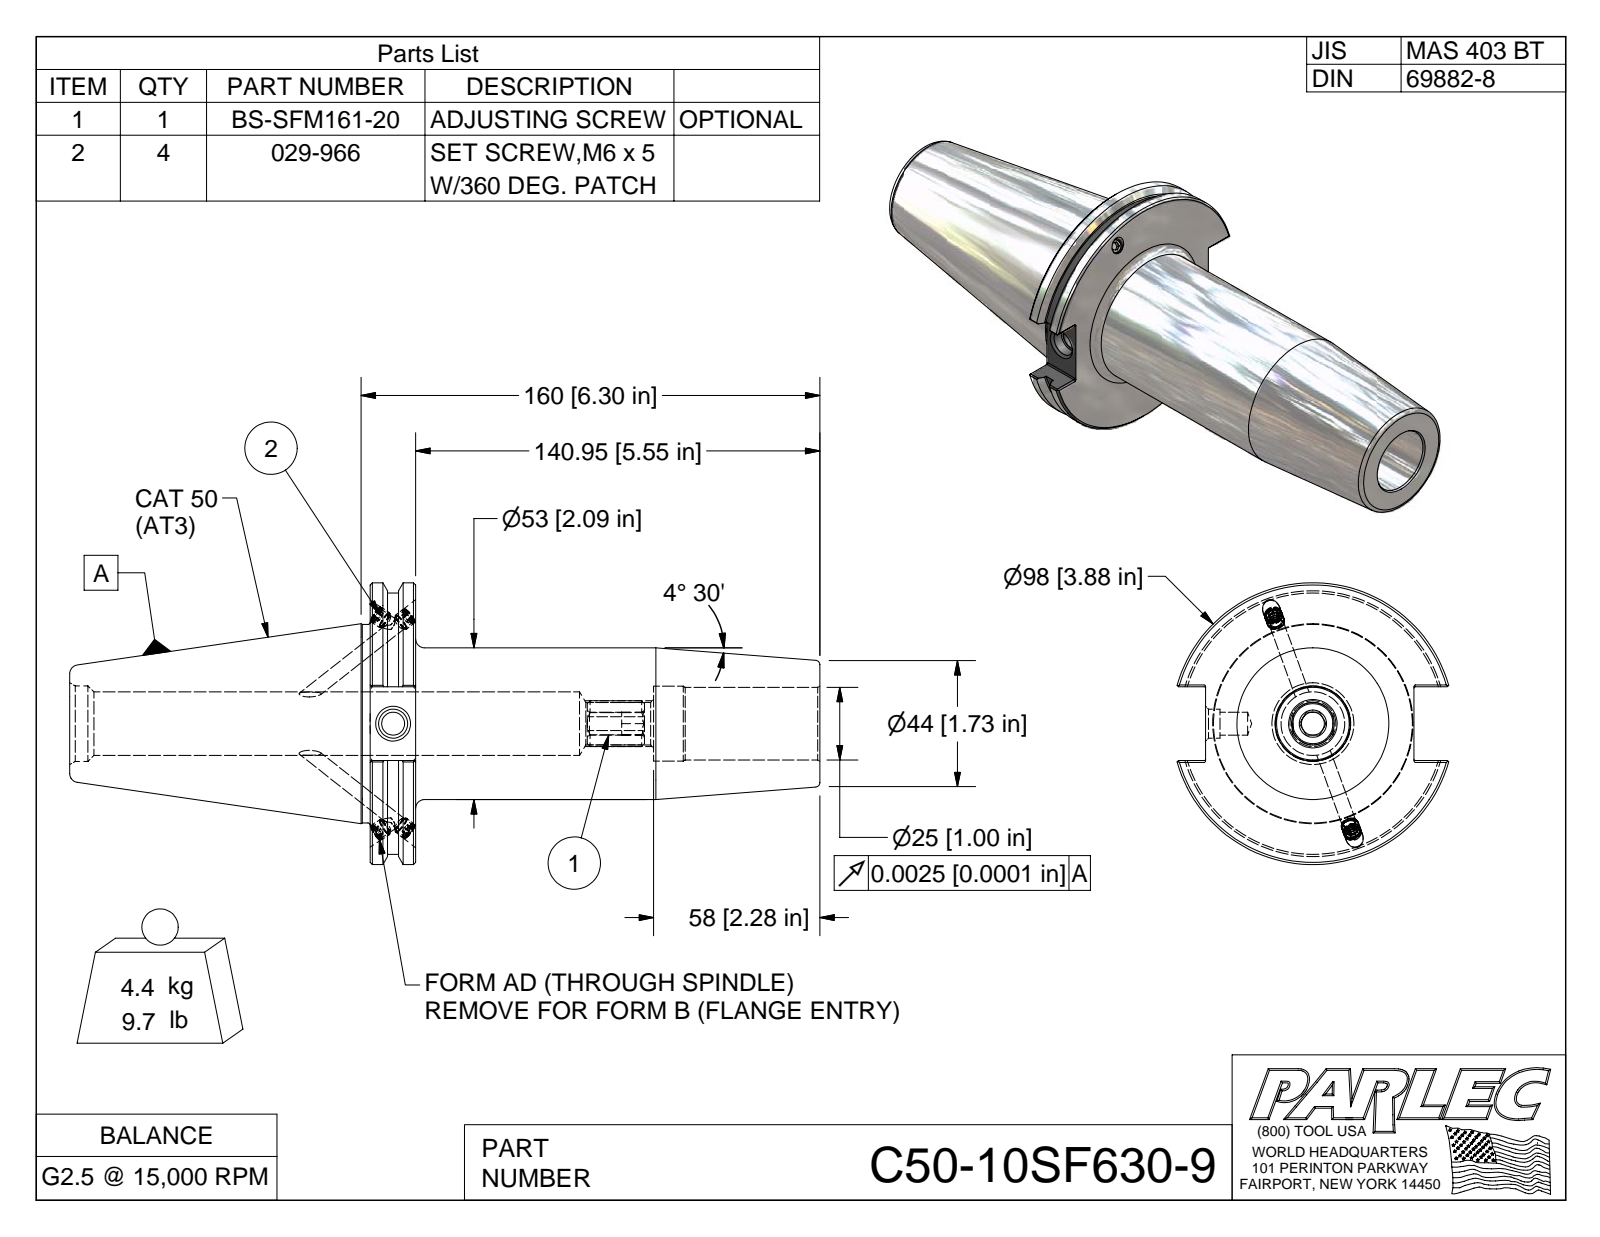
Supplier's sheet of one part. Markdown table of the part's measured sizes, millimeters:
| quantity | value |
| --- | --- |
| part name | C50-10SF630-9; C50BC-10SF630-9-1; BS-SFM161-20; 029-966 |
| STEP written by | Autodesk Inventor 2009 (AUTOMOTIVE_DESIGN) |
| units | millimeters |
| bodies | 6 solids, 186 faces (87 planar, 44 cylindrical, 55 other) |
| overall size | 261.6 × 98.4 × 94.7 |
| volume | 560 400 mm³ |
| surface area | 78 970 mm² |
| round holes (diameter × count) | 5 × 4, 6.1 × 4, 25.4 × 1, 26.1 × 1 |
| round bosses / shafts (diameter × count) | 6.2 × 4, 6 × 4, 98.4 × 1, 91.3 × 1, 69.3 × 1, 53 × 1 |
| partial cylindrical surfaces (radius × count) | 0.5 × 12, 8 × 1 |
| main face-to-face distances | 15.9, 156.8, 140.9, 104.8, 120.7, 261.6, 203.6, 98.8, 83, 58 |
